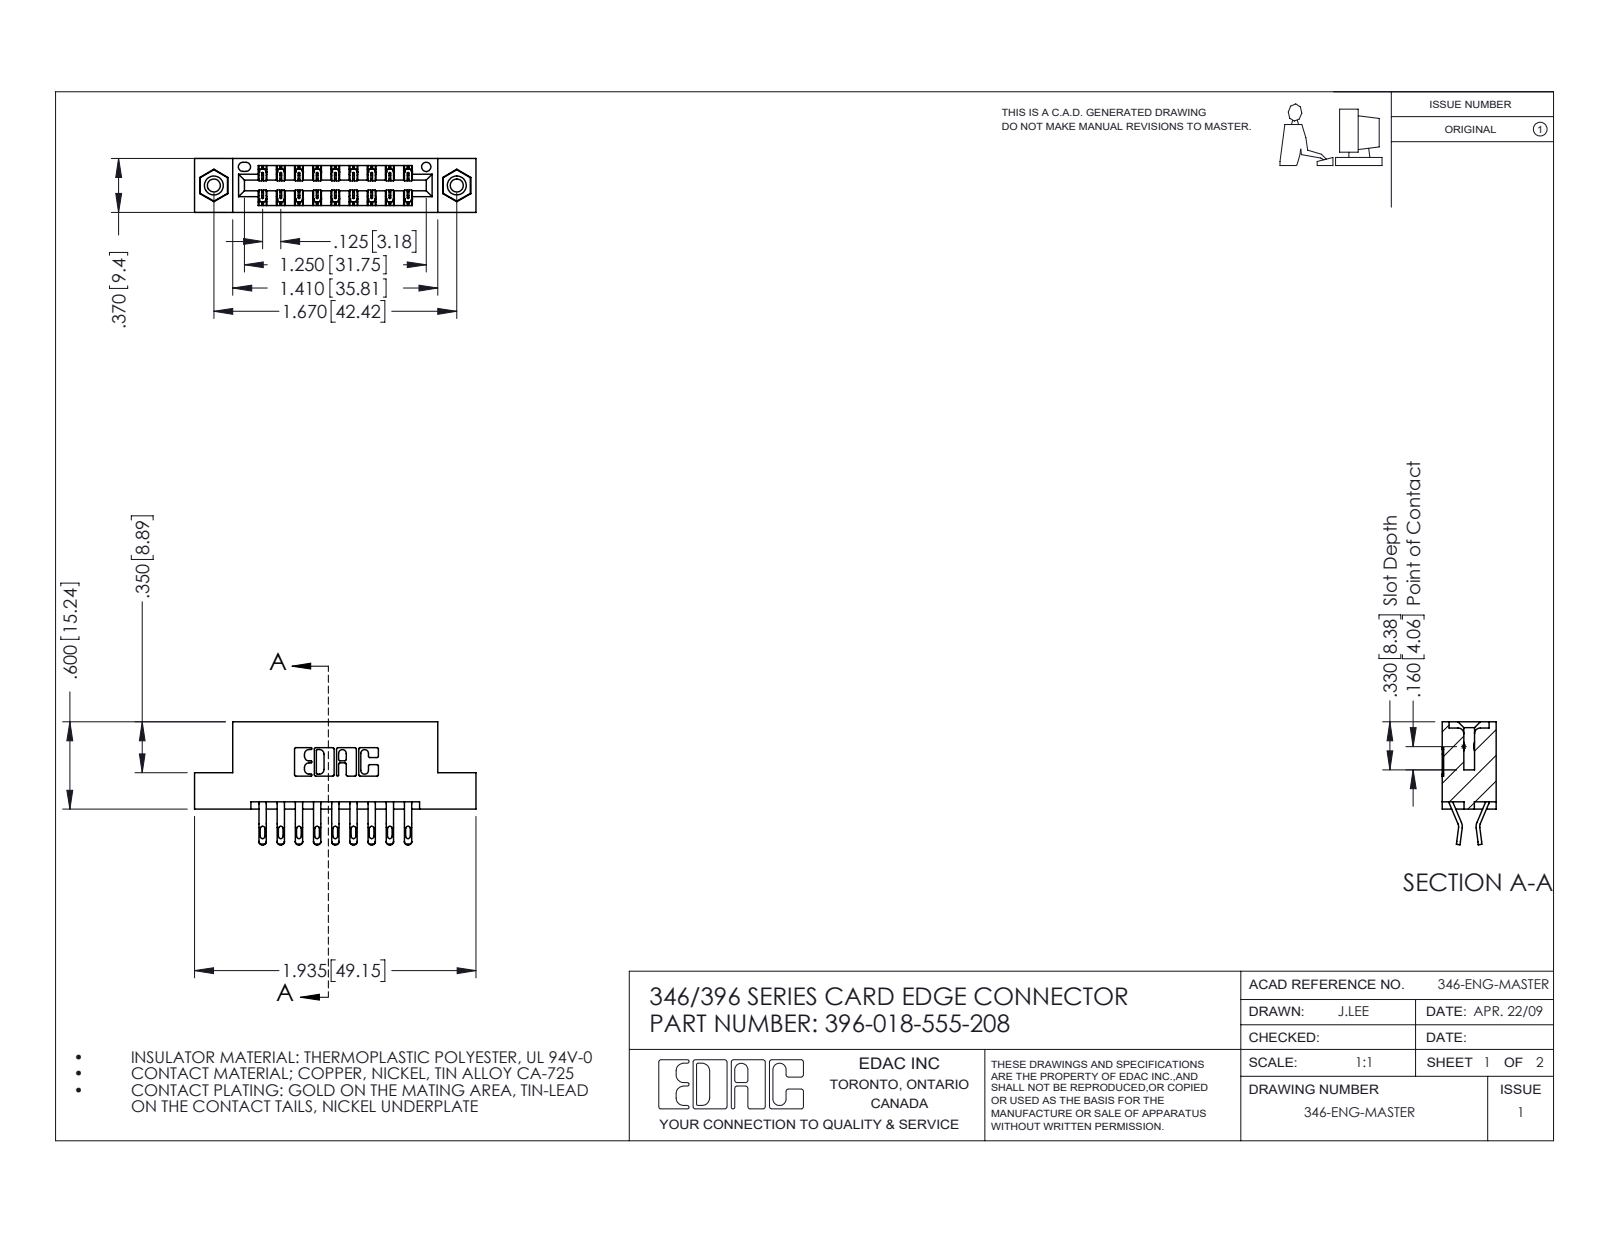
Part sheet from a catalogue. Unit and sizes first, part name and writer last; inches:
Units: inches
Overall size (bounding box): 1.935 × 0.845 × 0.37
Round holes (diameter × count): ⌀0.089 ×2, ⌀0.125 ×2, ⌀0.156 ×2, ⌀0.064 ×1
Round bosses / shafts (diameter × count): ⌀0.155 ×2
Partial cylindrical surfaces — rounded edges, fillets, slot ends (radius × count): R0.016 ×36, R0.02 ×36, R0.006 ×27, R0.01 ×22, R0.007 ×6, R0.031 ×6, R0.026 ×3, R0.01 ×2
Main face-to-face distances: 0.25, 0.048, 0.322, 0.37, 0.025, 0.072, 0.298, 0.148, 0.222, 0.1
Hole centre spacings: 0.246, 1.465, 1.67
Volume: 0.28 in³ · Surface area: 9.278 in²
Bodies: 21 solids, 1226 faces (702 planar, 508 cylindrical, 16 other)
Part name (STEP PRODUCT): 345-250-001_345-250-003-102; 346 Part_Flush Mounting Lugs - 0.156 Dia-TI; 396-018-555-208; 345-292-001_555 Tail
STEP written by: SolidWorks 2016 (CONFIG_CONTROL_DESIGN)
